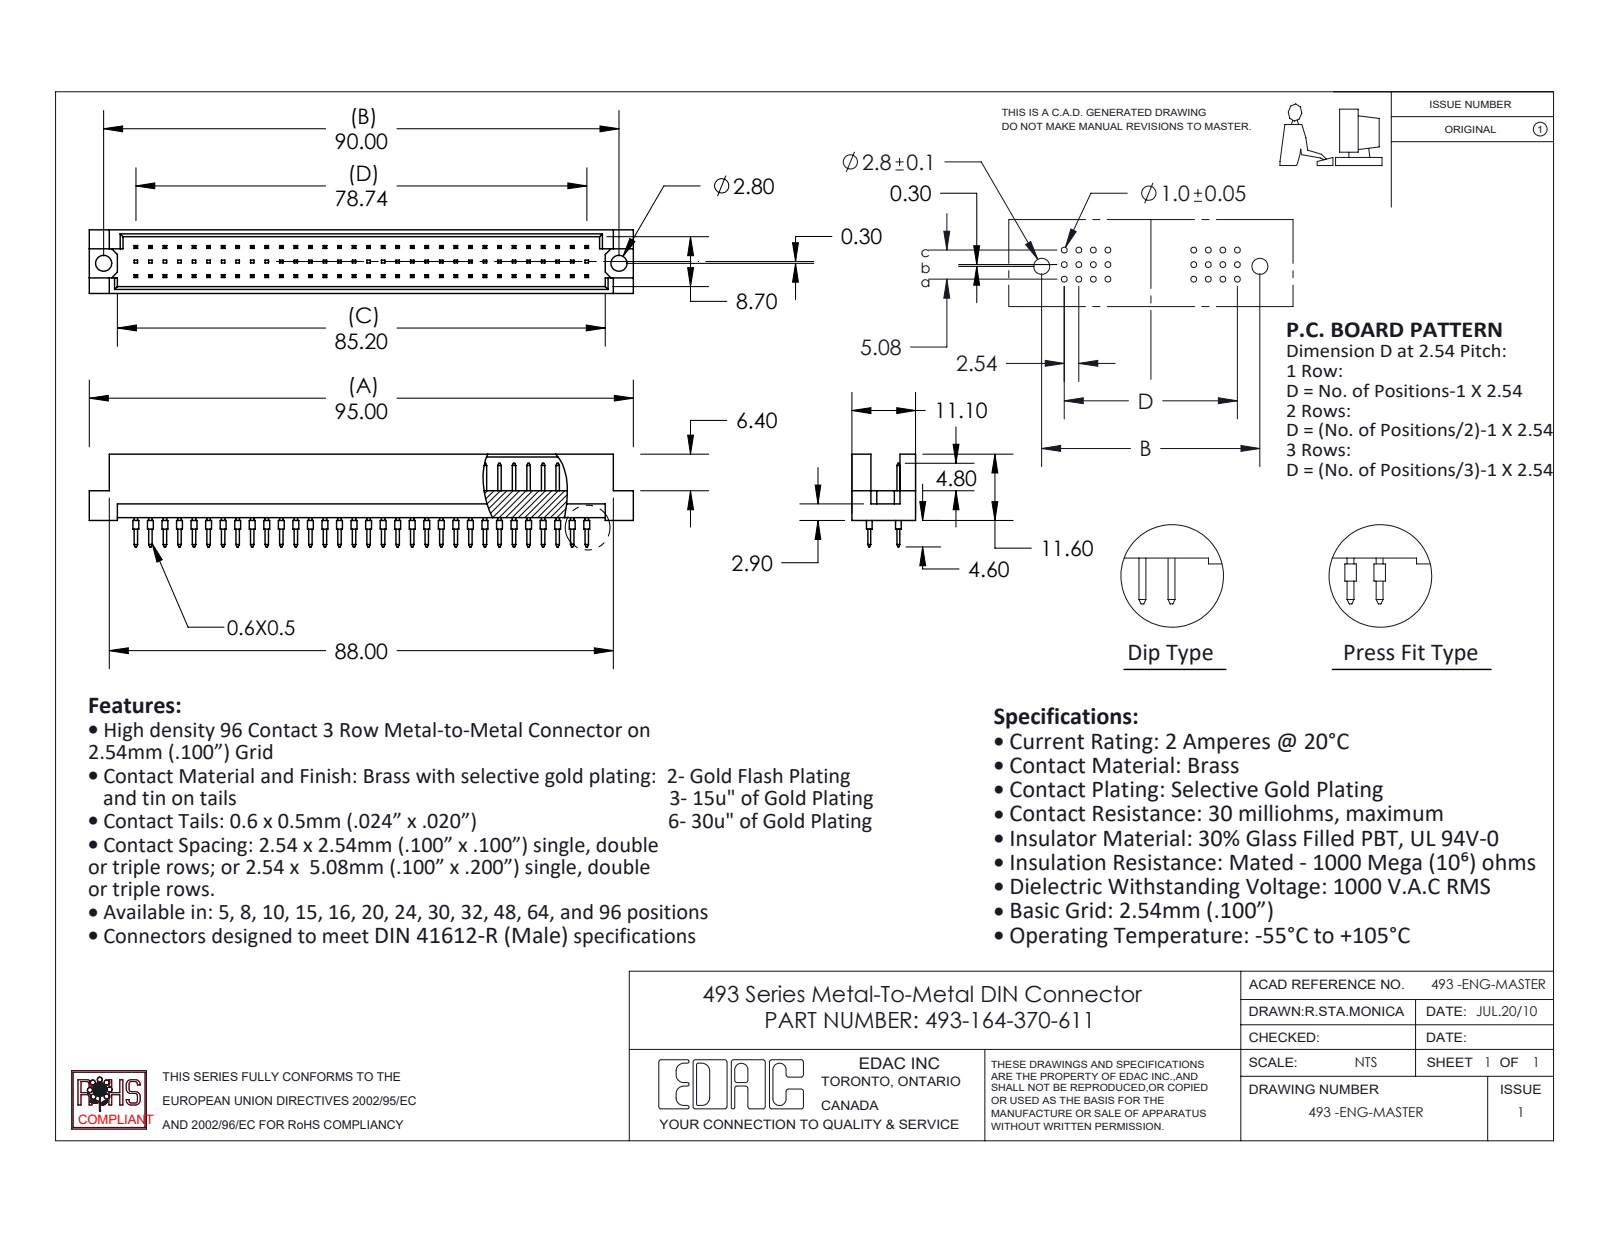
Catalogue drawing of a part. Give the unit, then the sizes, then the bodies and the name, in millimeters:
Units: millimetres
Overall size (bounding box): 95 × 16.2 × 11.1
Round holes (diameter × count): ⌀2.8 ×2
Round bosses / shafts (diameter × count): ⌀1 ×64
Main face-to-face distances: 1.2, 9.9, 11.1, 5.08, 0.5, 8.7, 4.7, 2.76, 3.26, 7.84
Hole centre spacings: 90
Volume: 5 979 mm³ · Surface area: 8 658 mm²
Bodies: 65 solids, 1844 faces (1712 planar, 132 cylindrical, 0 other)
Part name (STEP PRODUCT): 493-164-370-611; 493-290_70; 493 Part_96
STEP written by: SolidWorks 2020 (CONFIG_CONTROL_DESIGN)
